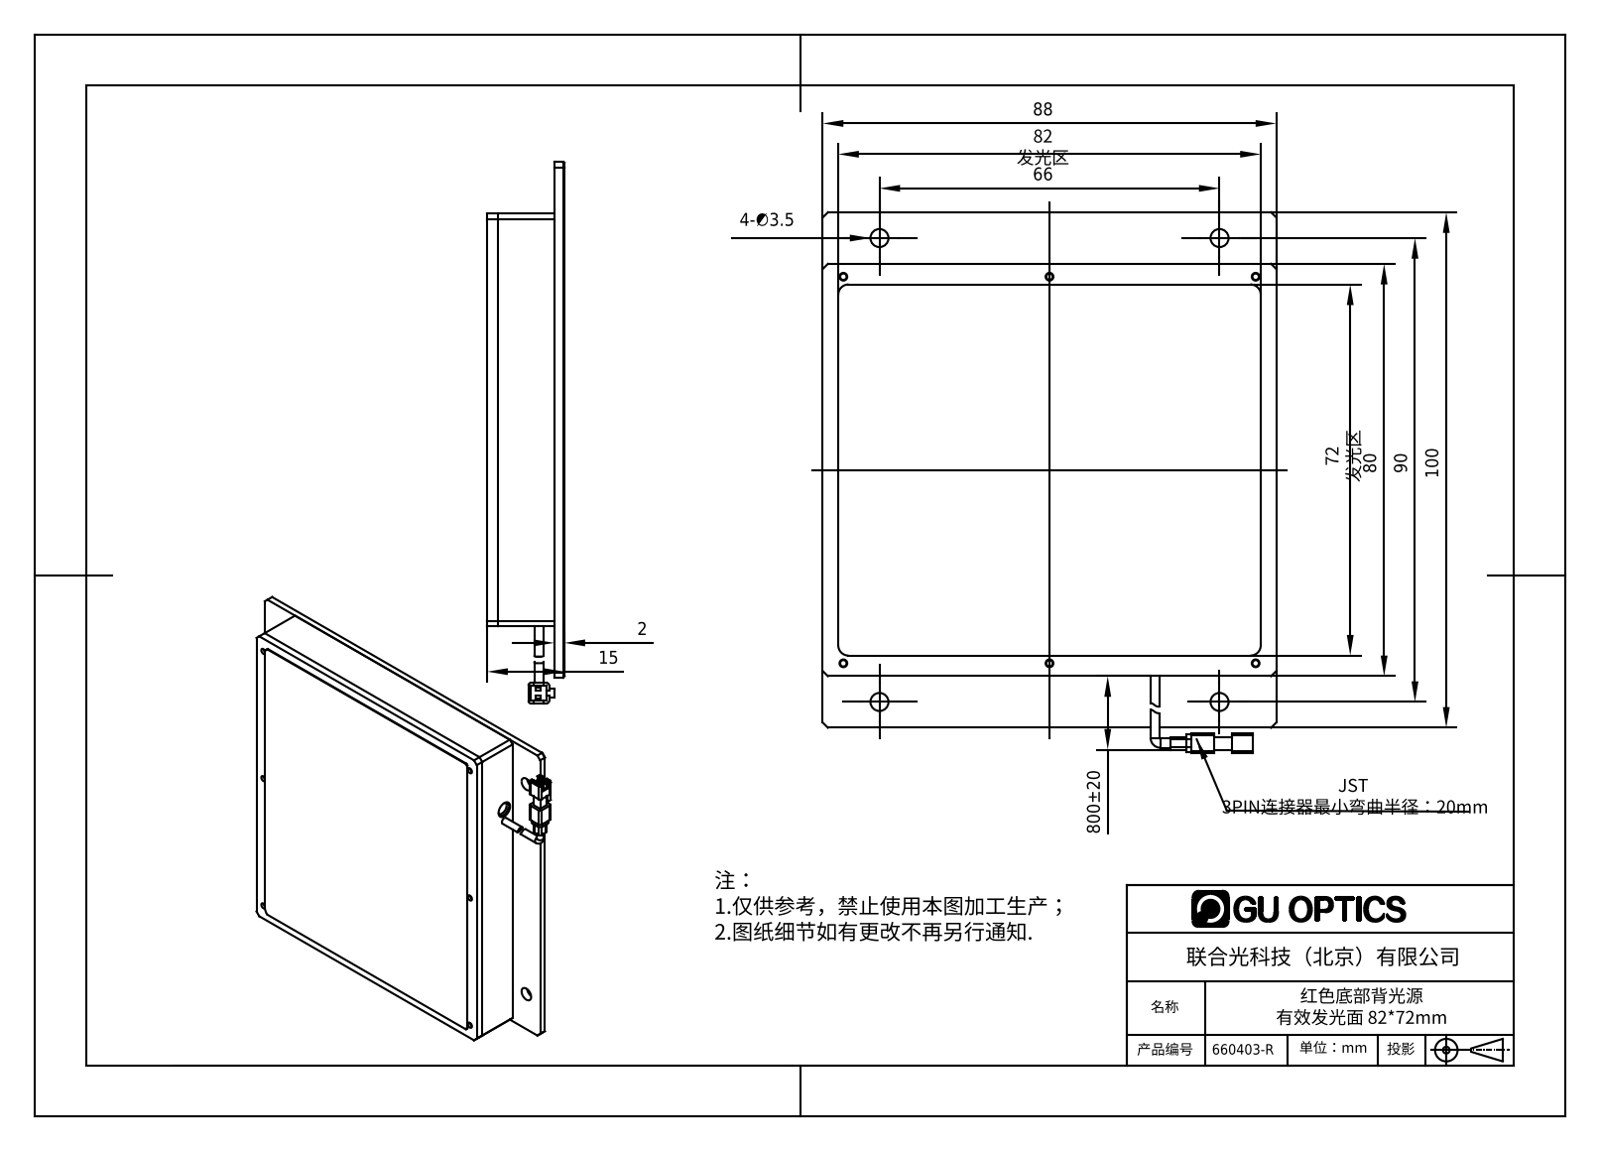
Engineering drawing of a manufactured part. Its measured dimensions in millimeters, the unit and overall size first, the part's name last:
Units: millimetres
Overall size (bounding box): 105 × 88 × 15.2
Round holes (diameter × count): ⌀1.25 ×12, ⌀1.6 ×12, ⌀1.5 ×6, ⌀2.4 ×6, ⌀2.8 ×6, ⌀3.5 ×4, ⌀3.6 ×1
Round bosses / shafts (diameter × count): ⌀1.75 ×2
Partial cylindrical surfaces — rounded edges, fillets, slot ends (radius × count): R0.5 ×8, R1 ×8, R2 ×4, R1.5 ×2, R0.65 ×1, R0.65 ×1, R1.71 ×1, R1.98 ×1
Main face-to-face distances: 2, 13, 11, 2.2, 15.2, 13.2, 3, 4, 76, 85
Hole centre spacings: 40, 80, 85.44, 0.5, 75.5, 9.9, 10.26, 33.73
Volume: 44 726 mm³ · Surface area: 43 208 mm²
Bodies: 5 solids, 421 faces (188 planar, 134 cylindrical, 99 other)
Part name (STEP PRODUCT): 660403-R
STEP written by: SolidWorks 2016 (AUTOMOTIVE_DESIGN)
